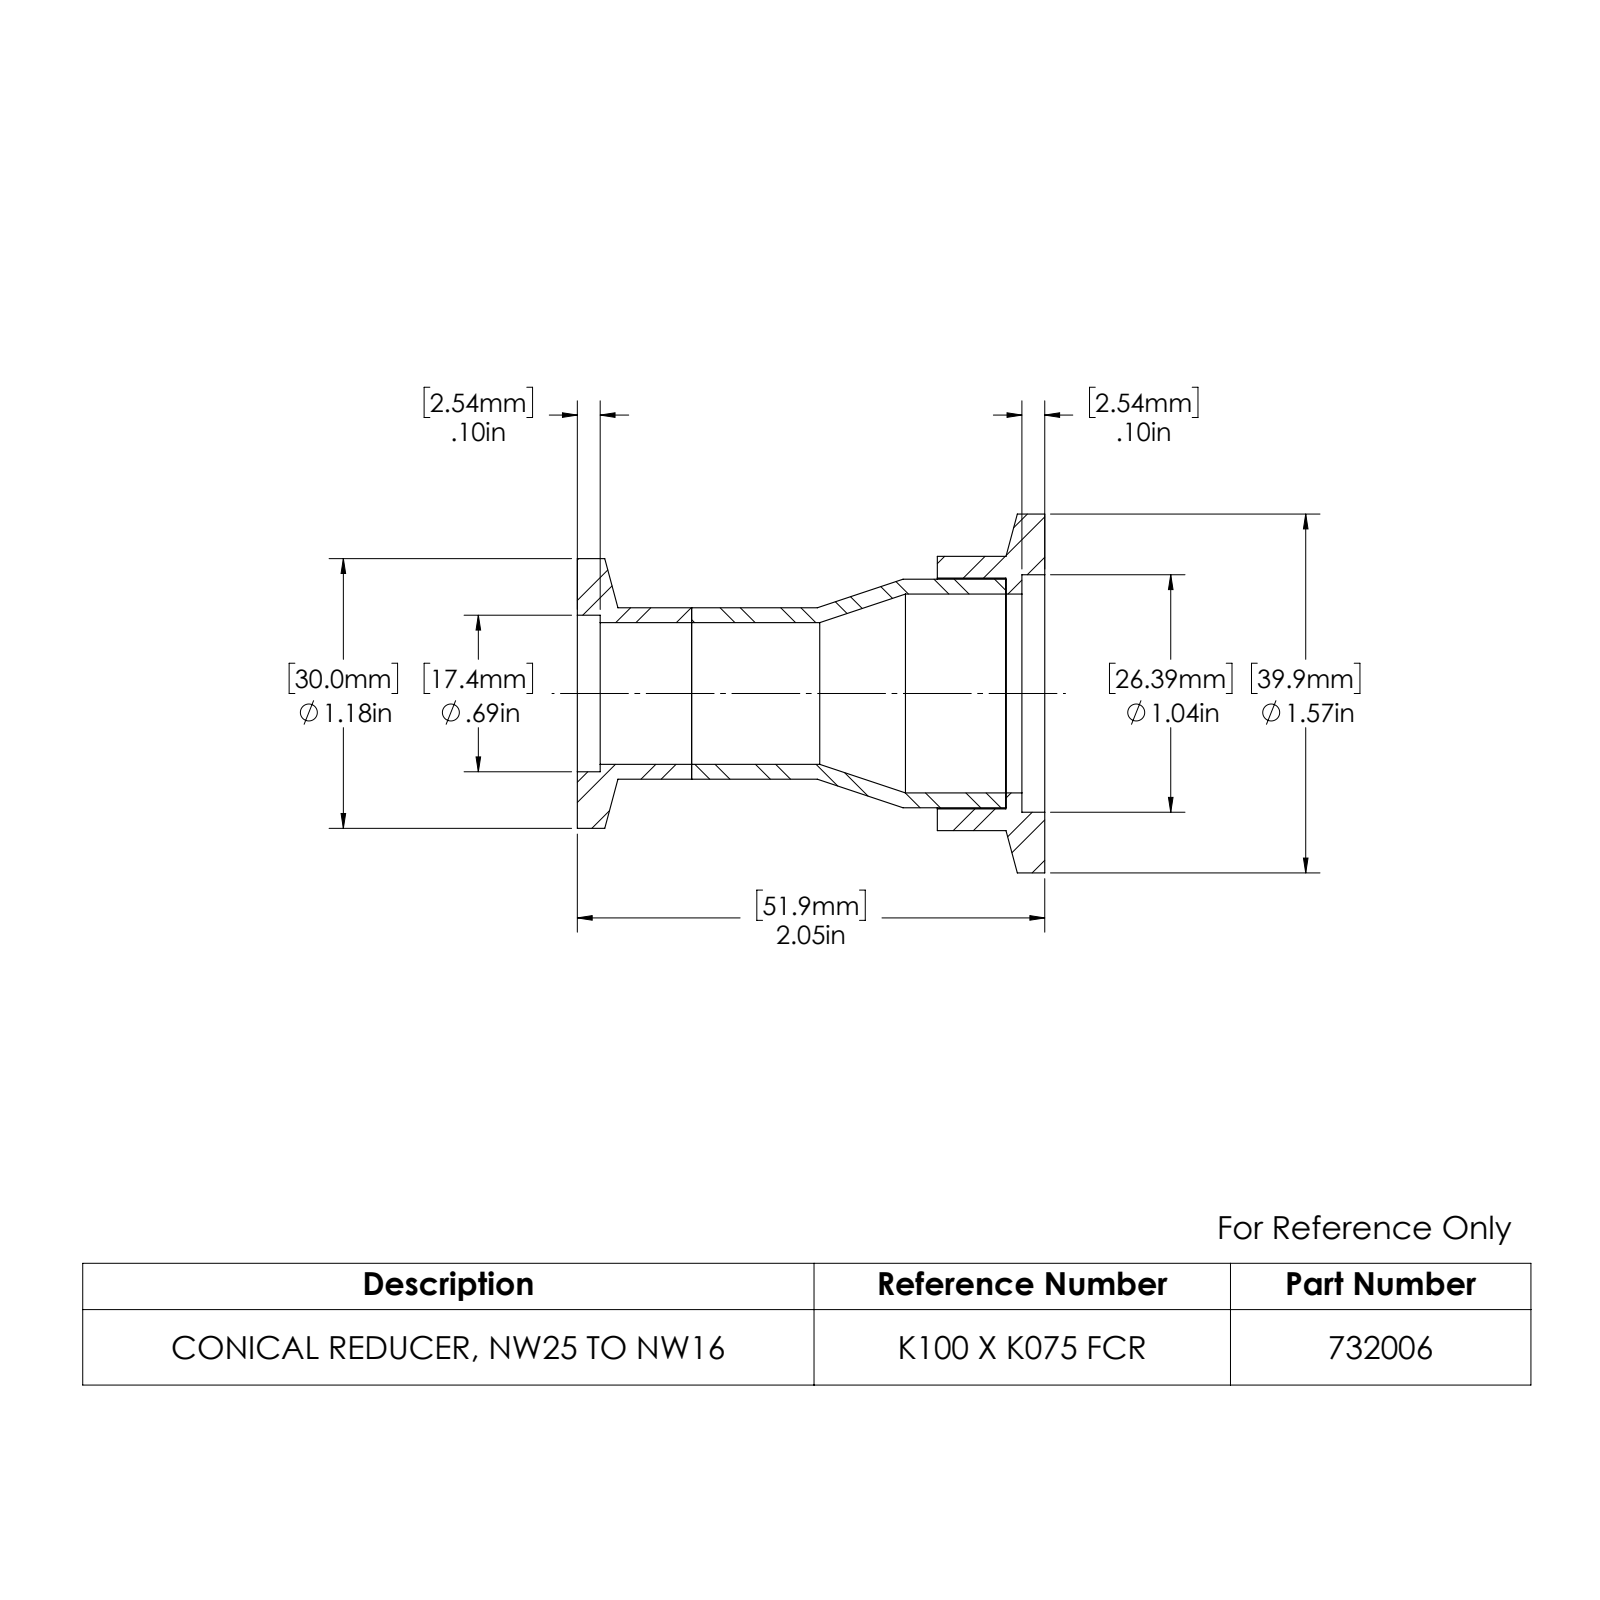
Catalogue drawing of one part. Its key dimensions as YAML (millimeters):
part_name: "715101; 732006_C; 402500; 713002"
step_written_by: "SolidWorks 2022 (CONFIG_CONTROL_DESIGN)"
units: millimeters
bodies: {solids: 3, faces: 43, planar: 9, cylindrical: 26, other: 8}
overall_size: [51.94, 39.88, 39.88]
volume: 10935
surface_area: 11004
round_holes:
  - {diameter: 15.75, count: 1}
  - {diameter: 17.4, count: 1}
  - {diameter: 22.1, count: 1}
  - {diameter: 25.65, count: 1}
  - {diameter: 26.39, count: 1}
round_bosses_or_shafts:
  - {diameter: 39.88, count: 1}
  - {diameter: 30.48, count: 1}
  - {diameter: 29.97, count: 1}
  - {diameter: 25.4, count: 1}
  - {diameter: 19.05, count: 1}
face_to_face_distances: [51.94, 4.31, 47.63, 11.93, 7.62, 40.01, 2.54, 49.4, 39.24, 34.93]
